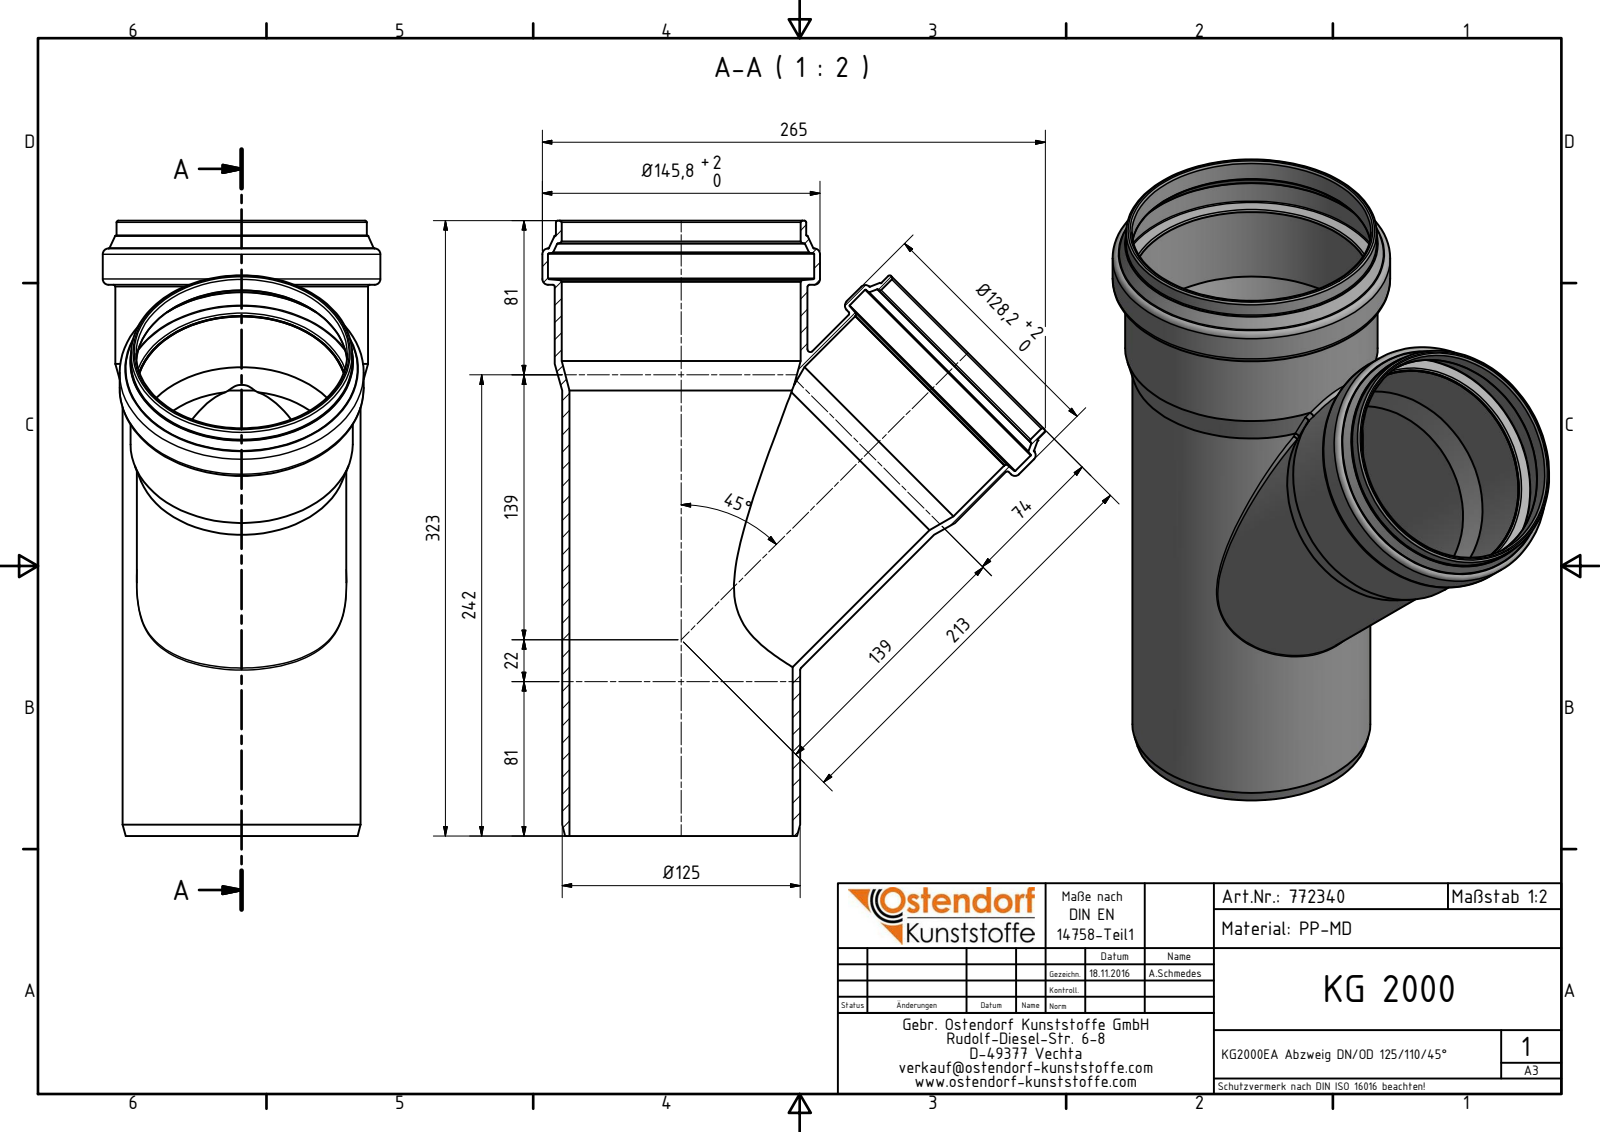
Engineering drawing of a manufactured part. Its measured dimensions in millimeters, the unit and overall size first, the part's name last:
Units: millimetres
Overall size (bounding box): 323 × 264.15 × 145.8
Round holes (diameter × count): ⌀103.2 ×1, ⌀110.5 ×1, ⌀110.74 ×1, ⌀110.9 ×1, ⌀117.2 ×1, ⌀123 ×1, ⌀125.5 ×1, ⌀139.8 ×1
Round bosses / shafts (diameter × count): ⌀145.8 ×1, ⌀132.7 ×1, ⌀131.5 ×1, ⌀128.2 ×1, ⌀125 ×1, ⌀116.7 ×1, ⌀116.1 ×1, ⌀110 ×1
Main face-to-face distances: 289.3, 323, 33.7, 29.1, 0.88, 28.22, 0.83, 28.27, 17.1, 16.27
Volume: 595 458 mm³ · Surface area: 341 533 mm²
Bodies: 1 solid, 78 faces (9 planar, 18 cylindrical, 51 other)
Part name (STEP PRODUCT): 772340 KG2000EA Abzweig DN_OD 125_110_45°
STEP written by: Autodesk Inventor 2016 (AUTOMOTIVE_DESIGN)
